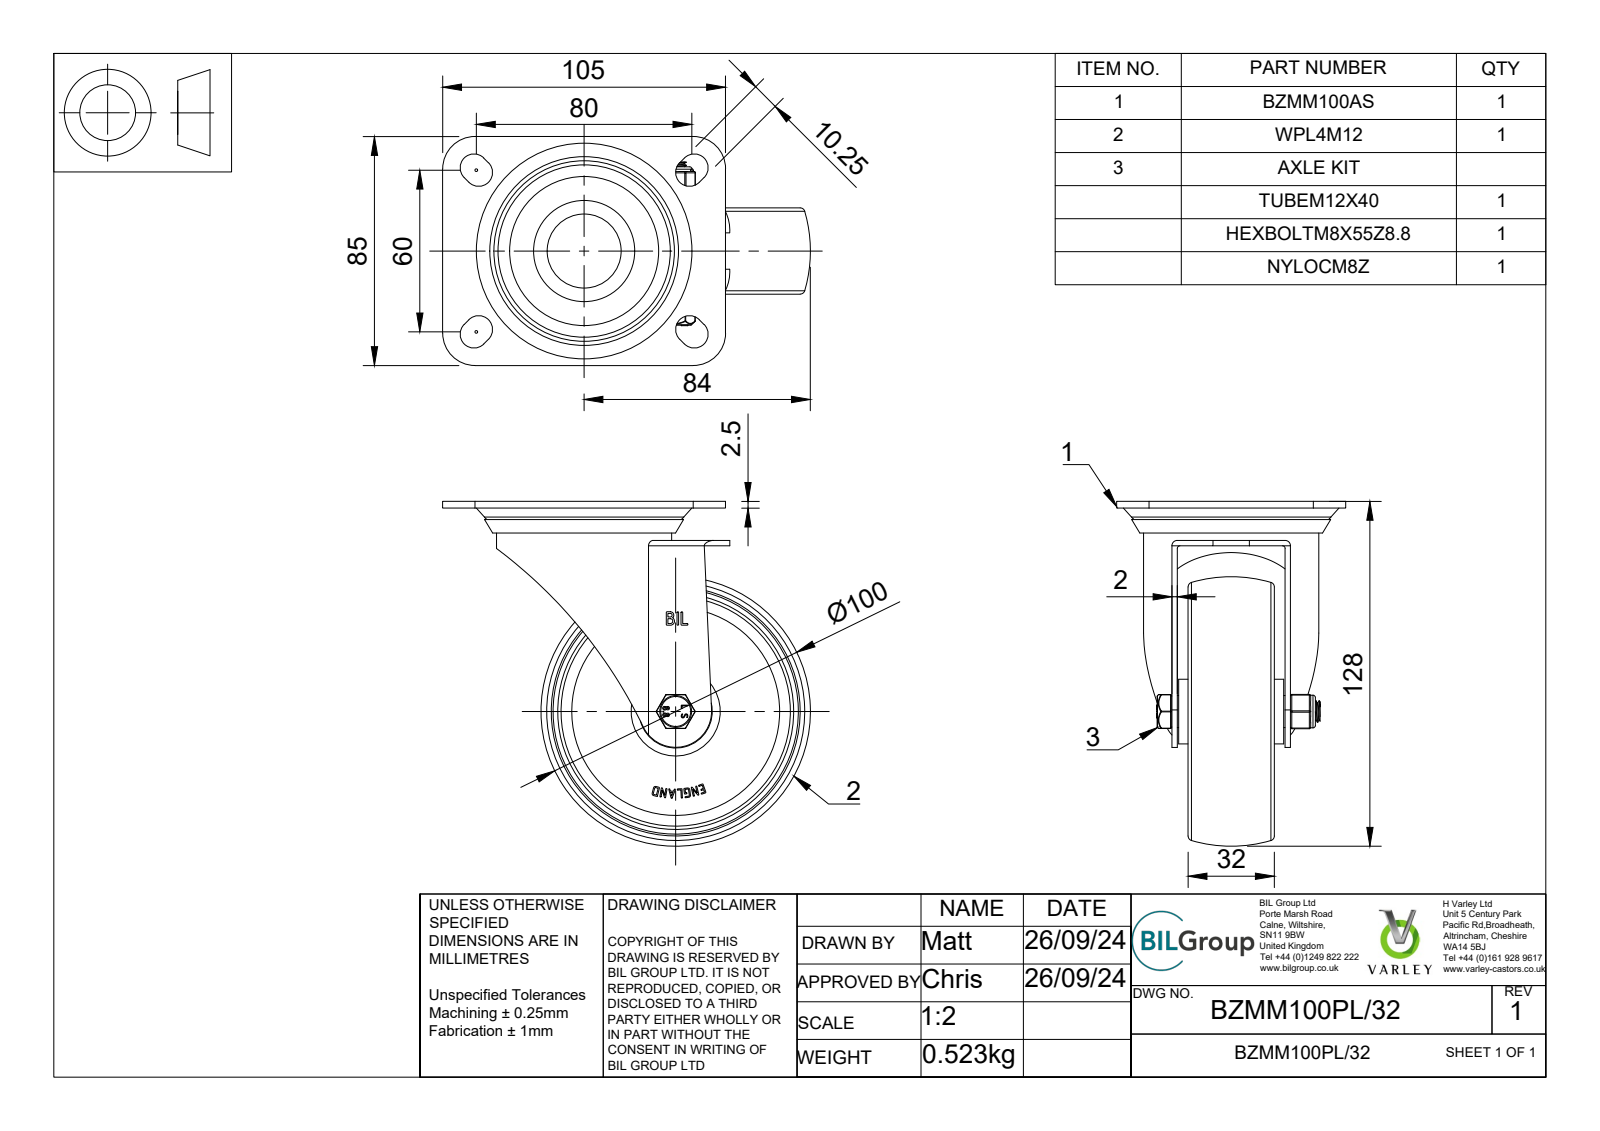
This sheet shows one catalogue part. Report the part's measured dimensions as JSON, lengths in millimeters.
{"part_name": "BZMM100PL/32 v3; BZMM100AS - 2 v2; ZINC PLATED, PRESSED STEEL TOP PLATE; ZINC PLATED, PRESSED STEEL TOP PLATE Geometry (+7 more)", "step_written_by": "Autodesk Translation Framework v13.20.0.188 (AUTOMOTIVE_DESIGN)", "units": "millimeters", "bodies": {"solids": 32, "faces": 512, "planar": 203, "cylindrical": 133, "other": 176}, "overall_size": [136.5, 128, 85], "volume_mm3": 170185, "surface_area_mm2": 89326, "round_holes": [[0.66, 2], [8, 1], [8.25, 1], [8.4, 1], [8.6, 1], [12.5, 1], [27.5, 1], [48, 1], [61, 1]], "round_bosses_or_shafts": [[65, 1], [31.5, 1], [24, 1], [12.1, 1], [11.9, 1], [11.5, 1], [7.87, 1], [6.45, 1]], "partial_cylinders_radius": [[0.5, 18], [0.25, 12], [5.12, 8], [0.33, 4], [0.64, 4], [1, 4], [12, 4], [0.63, 2]], "face_to_face_distances": [2, 2.5, 16.5, 7, 18.5, 25.5, 42, 23.5, 0.5, 14.5], "hole_center_spacings": [3.22, 2.49]}
